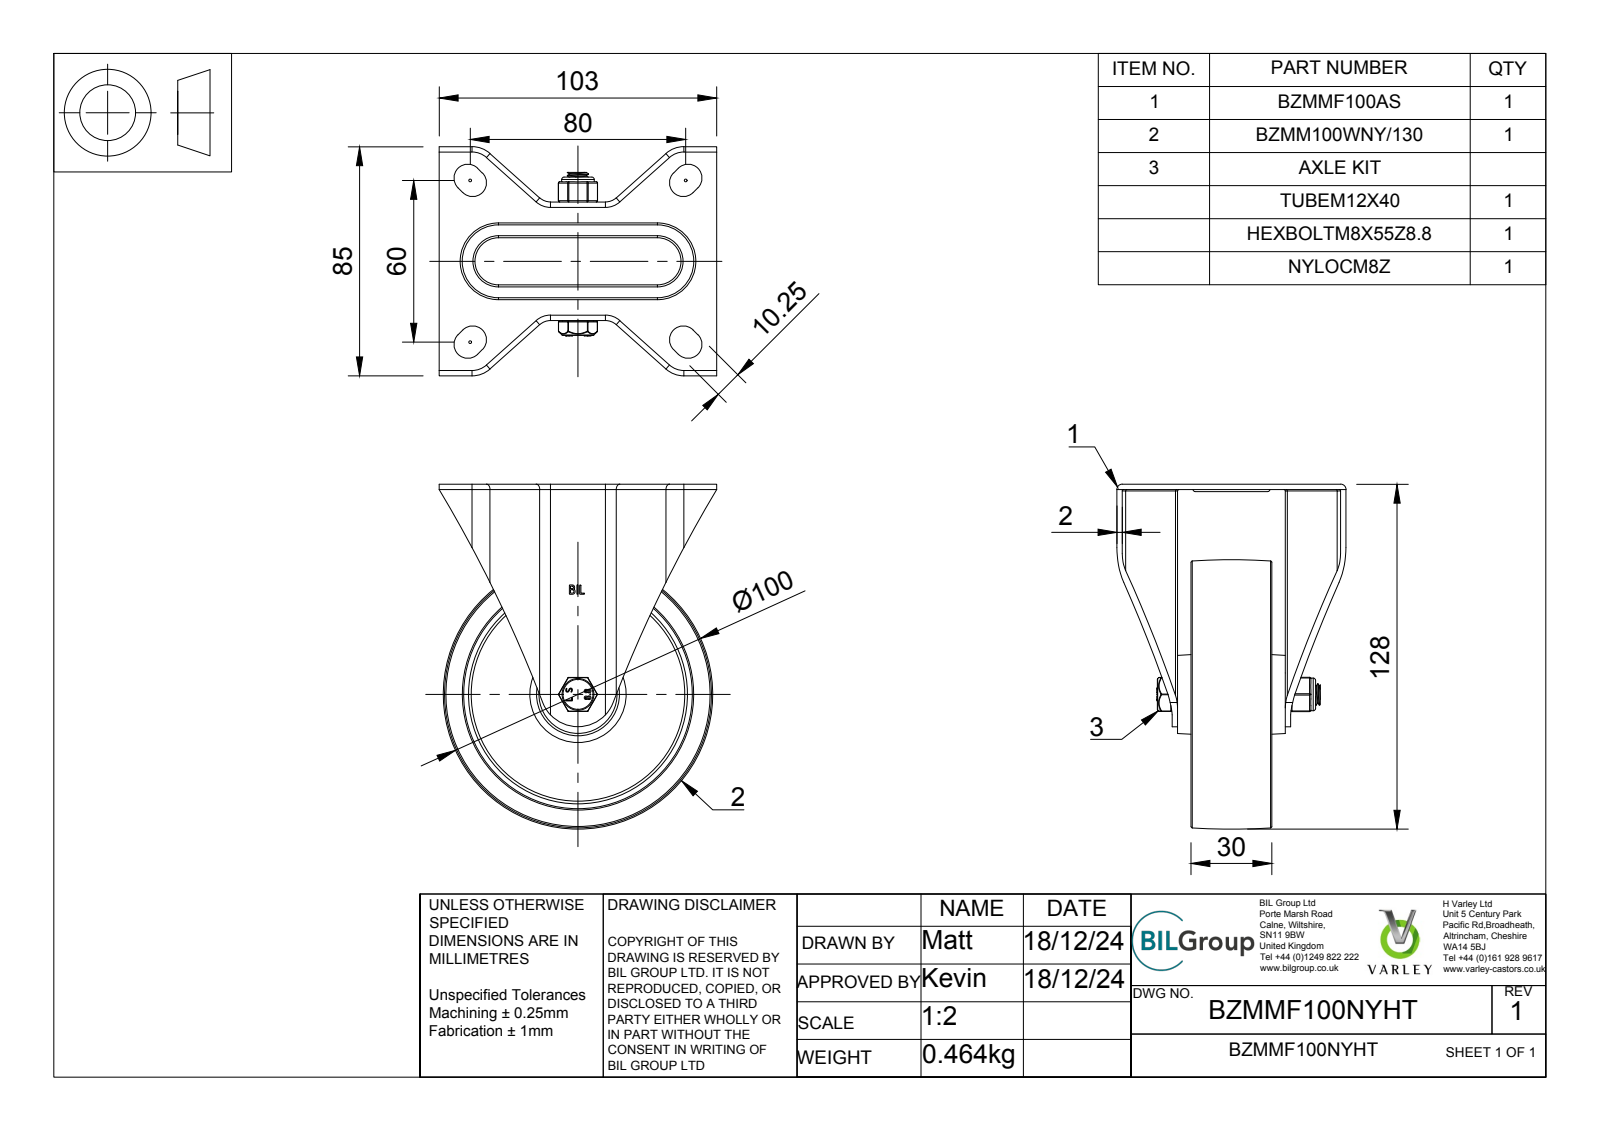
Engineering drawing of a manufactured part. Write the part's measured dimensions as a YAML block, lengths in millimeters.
part_name: "BZMMF100NYHT v4; BZMMF100AS v1; BZMMF100AS; ZINC PLATED, PRESSED STEEL BRACKET (+8 more)"
step_written_by: "Autodesk Translation Framework v13.20.0.188 (AP242_MANAGED_MODEL_BASED_3D_ENGINEERING_MIM_LF)"
units: millimeters
bodies: {solids: 6, faces: 387, planar: 123, cylindrical: 160, other: 104}
overall_size: [128, 103, 85]
volume: 151630
surface_area: 78309
round_holes:
  - {diameter: 0.66, count: 2}
  - {diameter: 8, count: 1}
  - {diameter: 8.25, count: 1}
  - {diameter: 8.4, count: 1}
  - {diameter: 8.6, count: 1}
  - {diameter: 12.5, count: 1}
round_bosses_or_shafts:
  - {diameter: 12.1, count: 1}
  - {diameter: 11.9, count: 1}
  - {diameter: 11.5, count: 1}
  - {diameter: 7.87, count: 1}
  - {diameter: 6.45, count: 1}
partial_cylinders:
  - {radius: 0.5, count: 26}
  - {radius: 0.25, count: 12}
  - {radius: 0.75, count: 8}
  - {radius: 2, count: 8}
  - {radius: 5.12, count: 8}
  - {radius: 0.33, count: 4}
  - {radius: 0.64, count: 4}
  - {radius: 3, count: 4}
face_to_face_distances: [2, 18.5, 14.26, 21.5, 20.5, 42, 3, 23.5, 5, 35]
hole_center_spacings: [3.22, 2.49]
